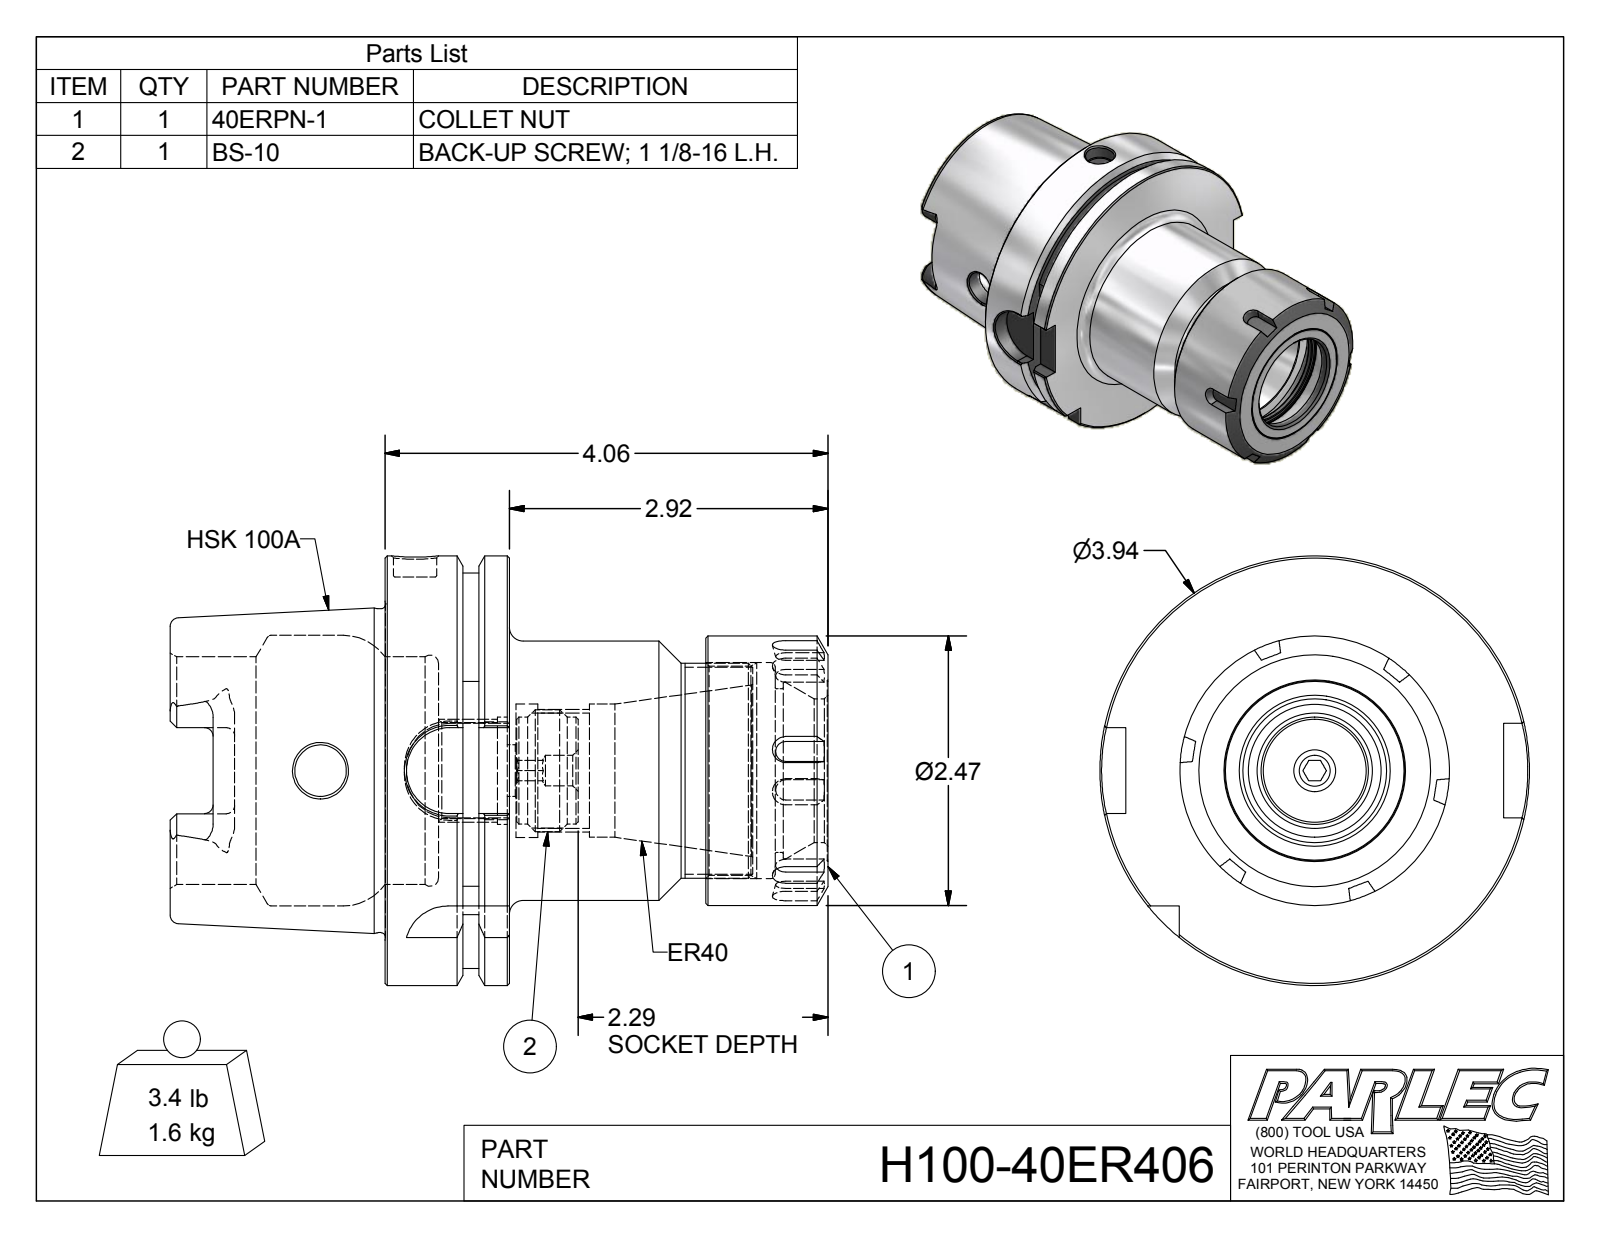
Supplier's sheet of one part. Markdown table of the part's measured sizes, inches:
| quantity | value |
| --- | --- |
| part name | H100-40ER406; H100-40ER4-1; BS-10; 40ERPN |
| STEP written by | Autodesk Inventor 2012 (AUTOMOTIVE_DESIGN) |
| units | inches |
| bodies | 3 solids, 199 faces (76 planar, 47 cylindrical, 76 other) |
| overall size | 6.029 × 3.937 × 3.937 |
| volume | 24.47 in³ |
| surface area | 125.5 in² |
| round holes (diameter × count) | 0.472 × 2, 0.22 × 1, 0.28 × 1, 0.394 × 1, 0.881 × 1, 0.985 × 1, 1.057 × 1, 1.22 × 1, 1.225 × 1, 1.318 × 1, 1.5 × 1, 1.62 × 1 |
| round bosses / shafts (diameter × count) | 3.937 × 1, 2.967 × 1, 2.47 × 1, 2.375 × 1, 1.969 × 1, 1.118 × 1, 0.98 × 1 |
| partial cylindrical surfaces (radius × count) | 0.079 × 6, 0.192 × 4, 0.394 × 4, 1.811 × 1 |
| main face-to-face distances | 1.142, 0.492, 0.65, 4.06, 3.568, 2.918, 2.94, 2.448, 1.798, 1.12 |
